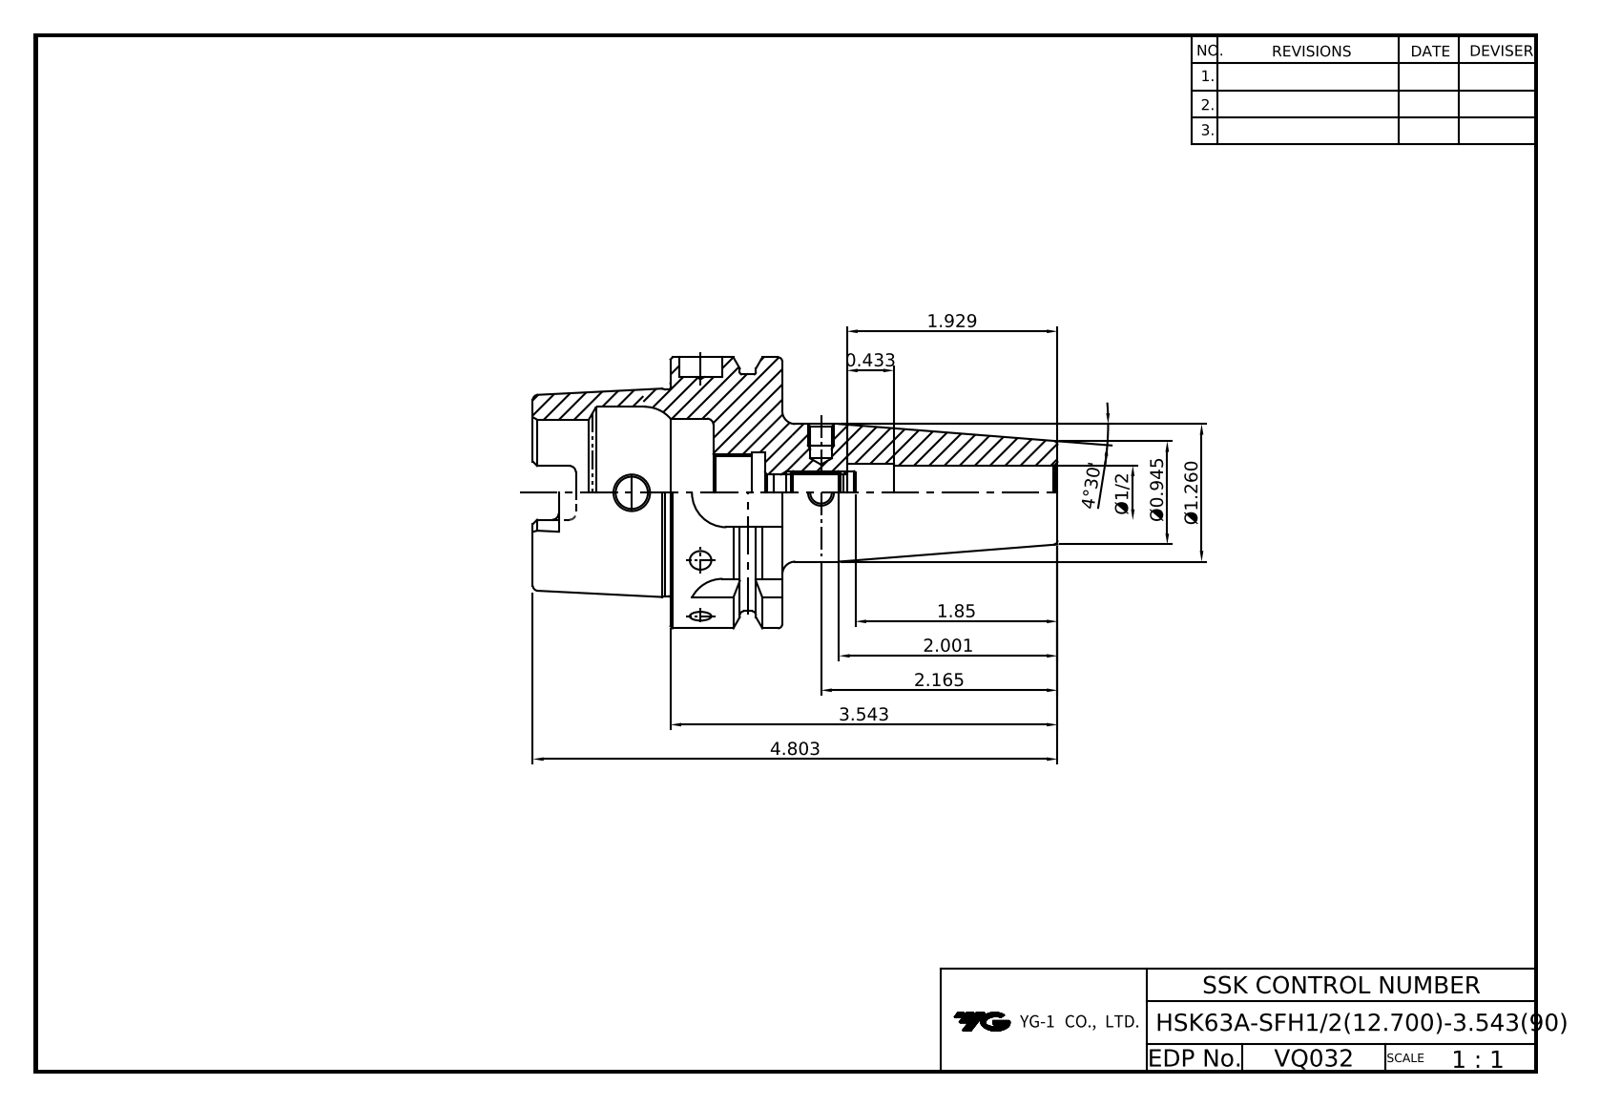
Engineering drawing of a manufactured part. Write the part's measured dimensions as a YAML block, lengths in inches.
part_name: "LO-HSK63A-SFH12.7-90"
step_written_by: "Autodesk Inventor 2022 (AUTOMOTIVE_DESIGN)"
units: inches
bodies: {solids: 1, faces: 118, planar: 44, cylindrical: 35, other: 39}
overall_size: [4.803, 2.48, 2.48]
volume: 7.091
surface_area: 46.72
round_holes:
  - {diameter: 0.295, count: 1}
  - {diameter: 0.331, count: 1}
  - {diameter: 0.351, count: 1}
  - {diameter: 0.394, count: 1}
  - {diameter: 0.441, count: 1}
  - {diameter: 0.5, count: 1}
  - {diameter: 0.547, count: 1}
  - {diameter: 0.666, count: 1}
  - {diameter: 0.748, count: 1}
  - {diameter: 1.339, count: 1}
  - {diameter: 1.575, count: 1}
round_bosses_or_shafts:
  - {diameter: 2.48, count: 1}
  - {diameter: 2.165, count: 1}
  - {diameter: 1.891, count: 1}
  - {diameter: 1.26, count: 1}
partial_cylinders:
  - {radius: 0.059, count: 6}
  - {radius: 0.113, count: 4}
  - {radius: 0.315, count: 4}
face_to_face_distances: [1.024, 0.394, 0.63, 1.26, 1.654, 2.283, 2.087, 0.866, 0.157, 0.472]
